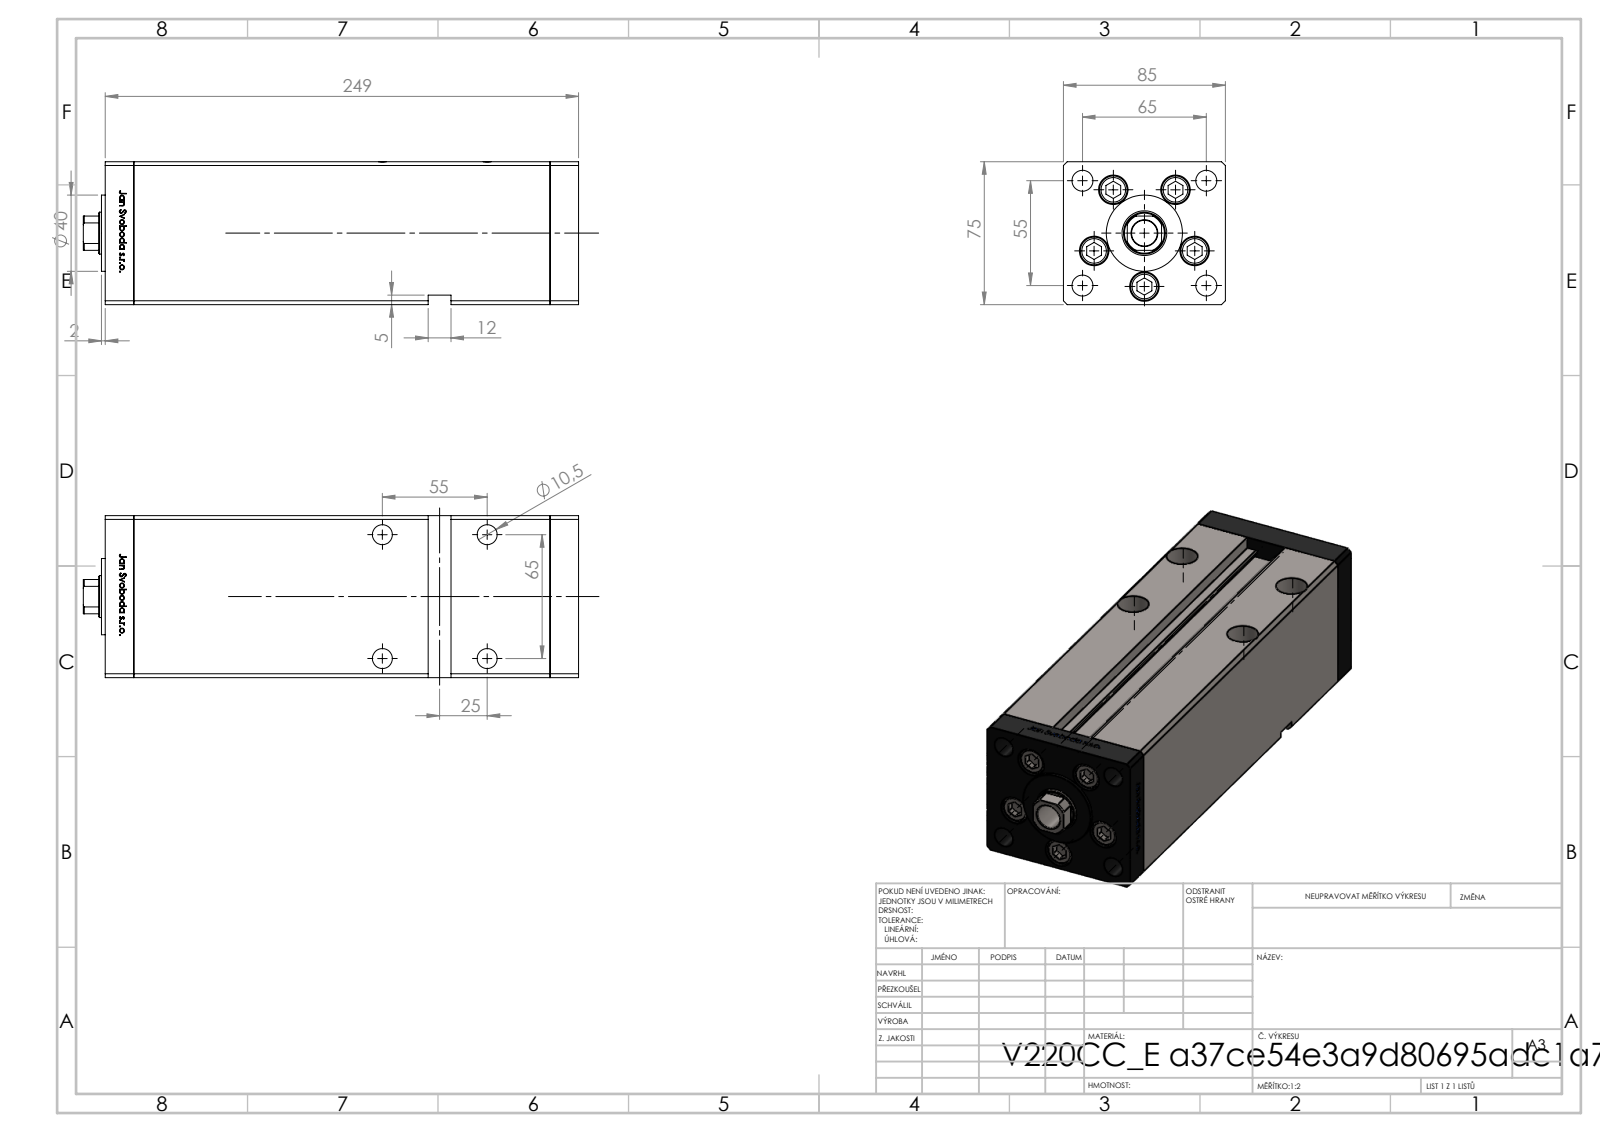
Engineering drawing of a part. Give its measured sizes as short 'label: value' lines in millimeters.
name: V220C_E MIDDLE; V220C_VC_E; V220C_FRONT_E; V220C BACK_E (+1 more)
written by: SolidWorks 2019 (CONFIG_CONTROL_DESIGN)
unit: mm
bodies: 13 solids, 1212 faces (473 planar, 165 cylindrical, 574 other)
size: 260 × 85 × 75
volume: 1 253 000 mm³; area: 209 534 mm²
holes: 9× ⌀11, 5× ⌀15.5, 4× ⌀10.5, 4× ⌀16.5, 2× ⌀2, 2× ⌀13.16, 1× ⌀13.5, 1× ⌀22, 1× ⌀23.5
bosses: 5× ⌀14.5, 5× ⌀8, 1× ⌀40
rounds: 2× R0.93, 1× R10.5
face distances: 85, 75, 15, 218.5, 233.5, 10.5, 248.5, 68.5, 34.25, 64.5
hole spacings: 28, 42.57, 55, 65, 85.15, 16.86, 19.17, 32.33
